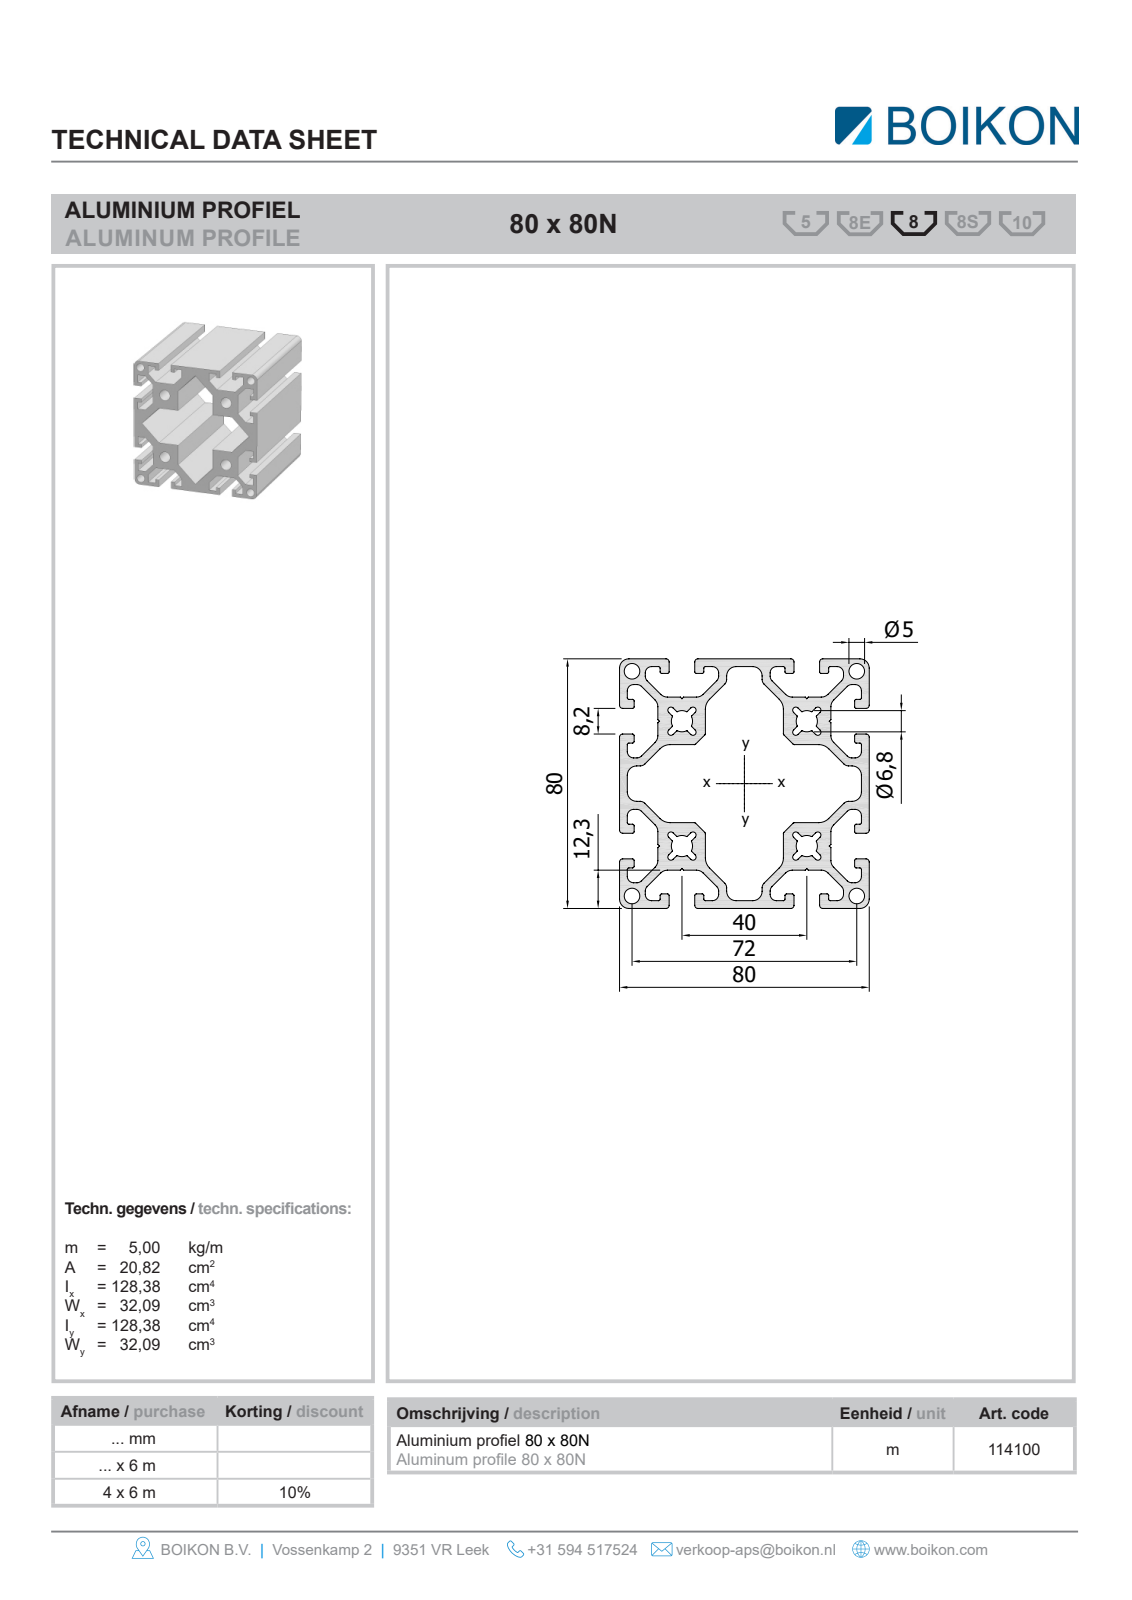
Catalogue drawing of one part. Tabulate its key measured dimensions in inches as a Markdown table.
| quantity | value |
| --- | --- |
| part name | Root; 11410080x80NBOIKON0 |
| STEP written by | HiCAD 2013 1802.4 Build 509 (AUTOMOTIVE_DESIGN) |
| units | inches |
| bodies | 1 solid, 146 faces (134 planar, 12 cylindrical, 0 other) |
| overall size | 39.37 × 3.15 × 3.15 |
| volume | 146.6 in³ |
| surface area | 1 762 in² |
| round holes (diameter × count) | 0.197 × 4, 0.268 × 4 |
| partial cylindrical surfaces (radius × count) | 0.118 × 4 |
| main face-to-face distances | 0.089, 1.132, 3.15, 1.929, 1.043, 2.018, 0.482, 2.667, 0.65, 1.535 |
| hole center spacings | 2.293, 0.891, 1.575, 2.835, 3.118, 2.227, 4.009 |
